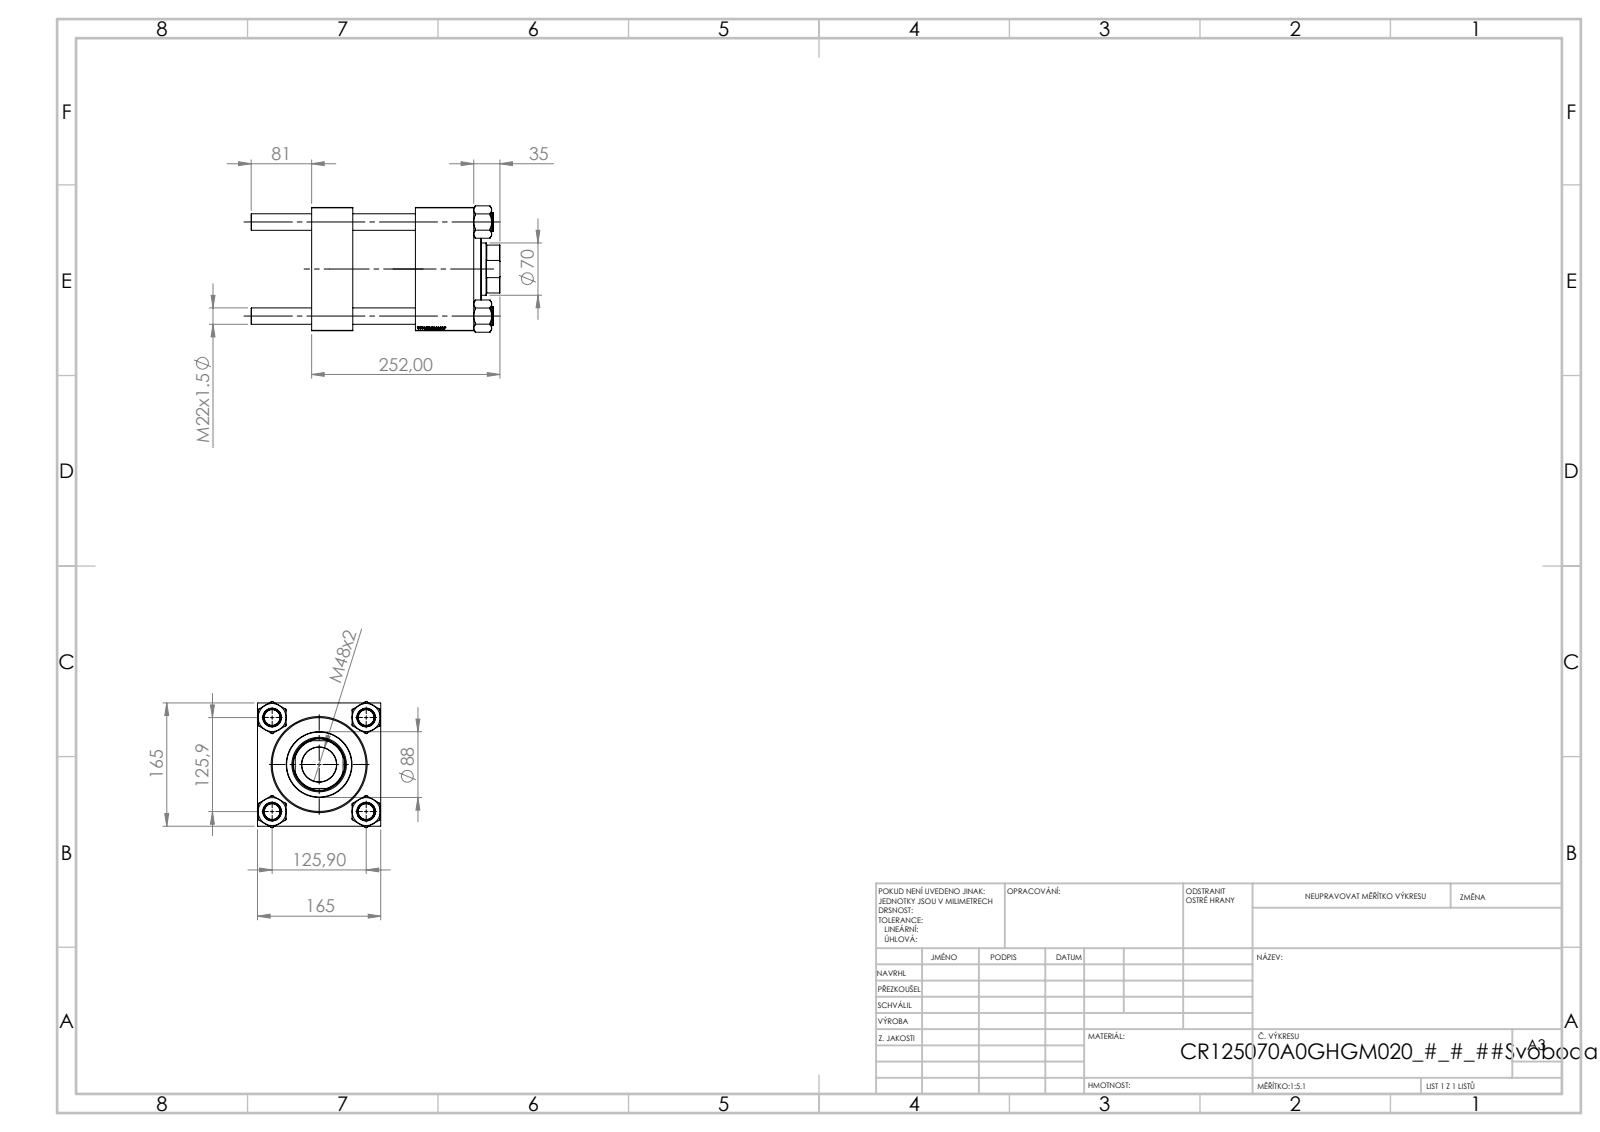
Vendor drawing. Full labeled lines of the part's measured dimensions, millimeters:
Part name (STEP PRODUCT): CR025_012_A_0_G_A_G_M_020_+#_##_TYCINKA; V215_VC_A; V215CR_BODY_A; NUT_M5 (+1 more)
STEP written by: SolidWorks 2019 (CONFIG_CONTROL_DESIGN)
Units: millimetres
Bodies: 10 solids, 257 faces (107 planar, 42 cylindrical, 108 other)
Overall size (bounding box): 333 × 169.14 × 163.35
Volume: 2 007 000 mm³ · Surface area: 246 981 mm²
Round holes (diameter × count): ⌀22 ×4, ⌀46.5 ×1, ⌀70 ×1, ⌀73 ×1
Round bosses / shafts (diameter × count): ⌀25 ×4, ⌀125.5 ×1, ⌀125 ×1, ⌀88 ×1
Partial cylindrical surfaces — rounded edges, fillets, slot ends (radius × count): R34 ×1
Main face-to-face distances: 64, 162, 133.3, 28.7, 69.3, 98, 37.44, 62.95, 109.03, 24
Hole centre spacings: 89.02, 125.9, 178.05
